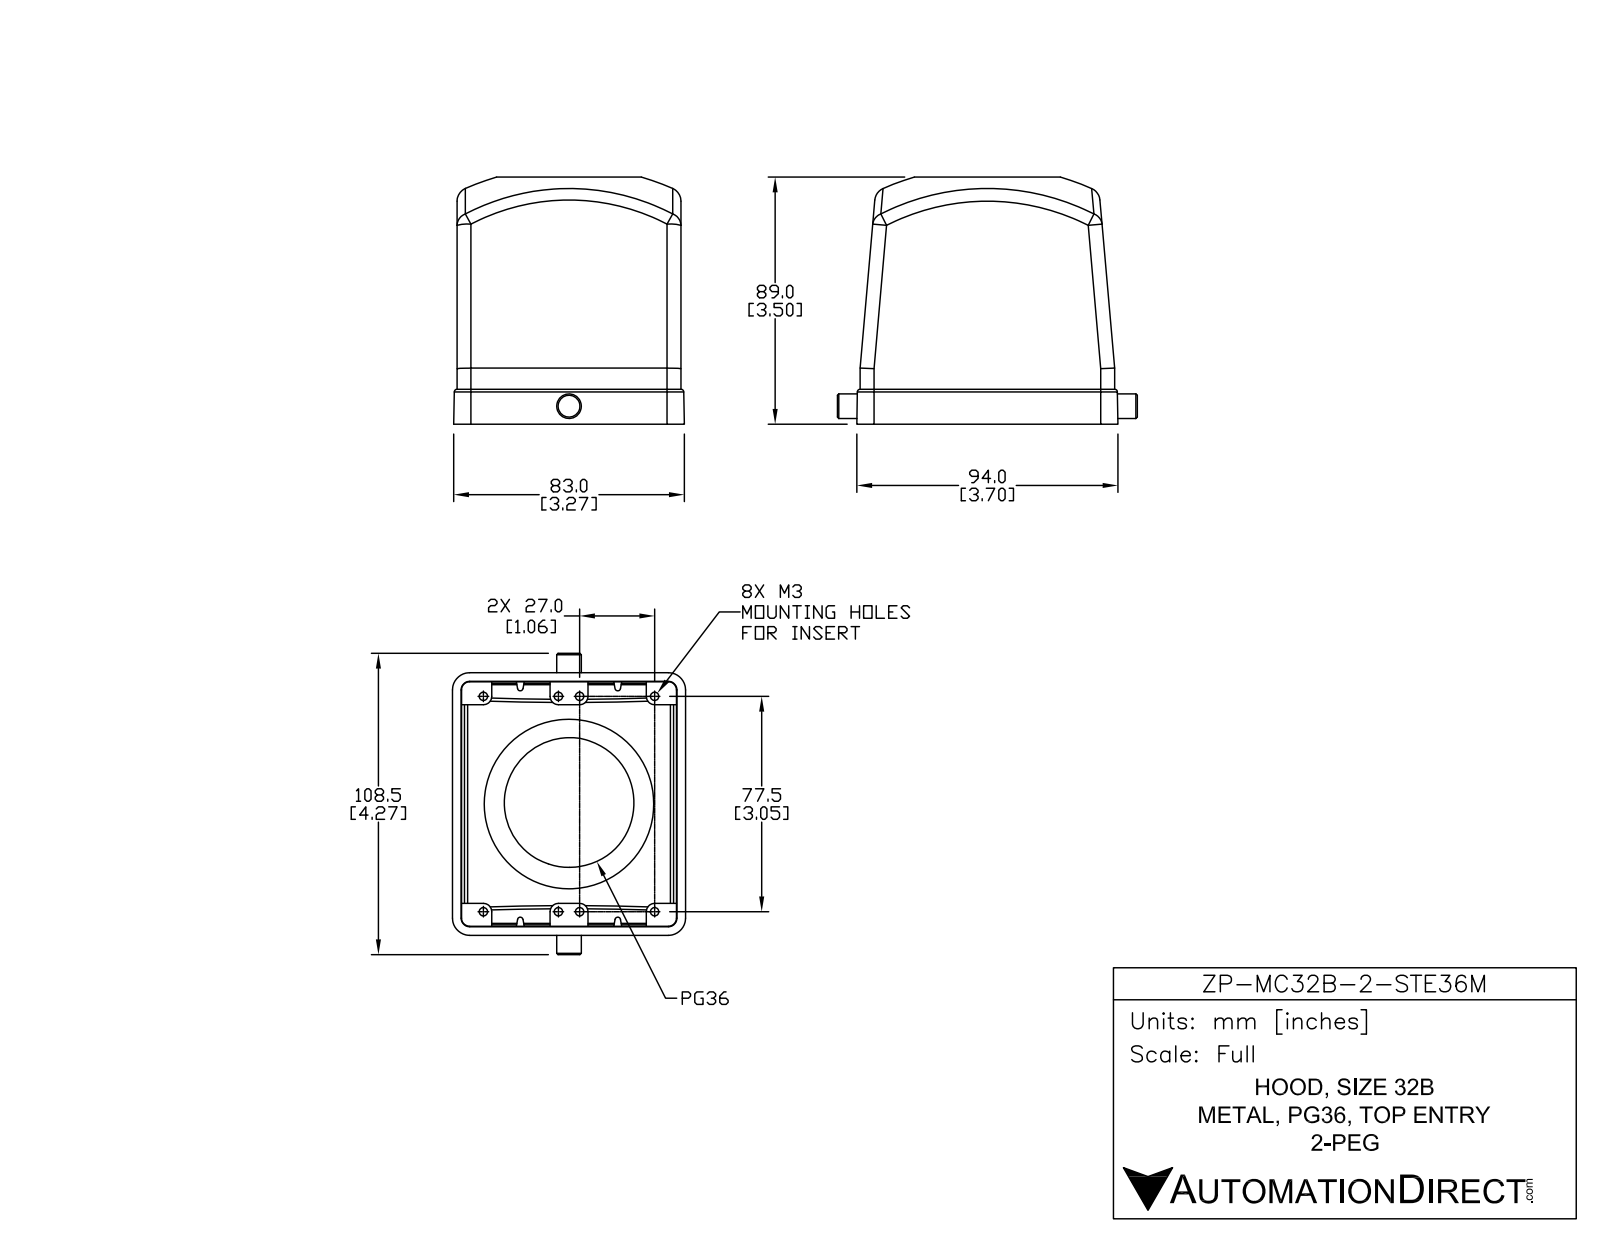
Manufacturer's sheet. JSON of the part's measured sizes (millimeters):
{"part_name": "ZP-MC32B-2-STE36M", "step_written_by": "SolidWorks 2014 (AUTOMOTIVE_DESIGN)", "units": "millimeters", "bodies": {"solids": 1, "faces": 194, "planar": 85, "cylindrical": 72, "other": 37}, "overall_size": [108.45, 92.75, 83.9], "volume_mm3": 126802, "surface_area_mm2": 69982, "round_holes": [[3, 8], [2.65, 1], [45.6, 1], [53, 1]], "round_bosses_or_shafts": [[61, 1], [8.85, 1]], "partial_cylinders_radius": [[1, 8], [3, 8], [5, 8], [0.5, 4]], "face_to_face_distances": [3.1, 78.4, 81.5, 75.3, 10.3, 81.8, 71.5, 85.65, 89, 7.2], "hole_center_spacings": [27, 34.64, 38.94, 49.51, 77.5, 82.07, 84.89, 7.64]}
